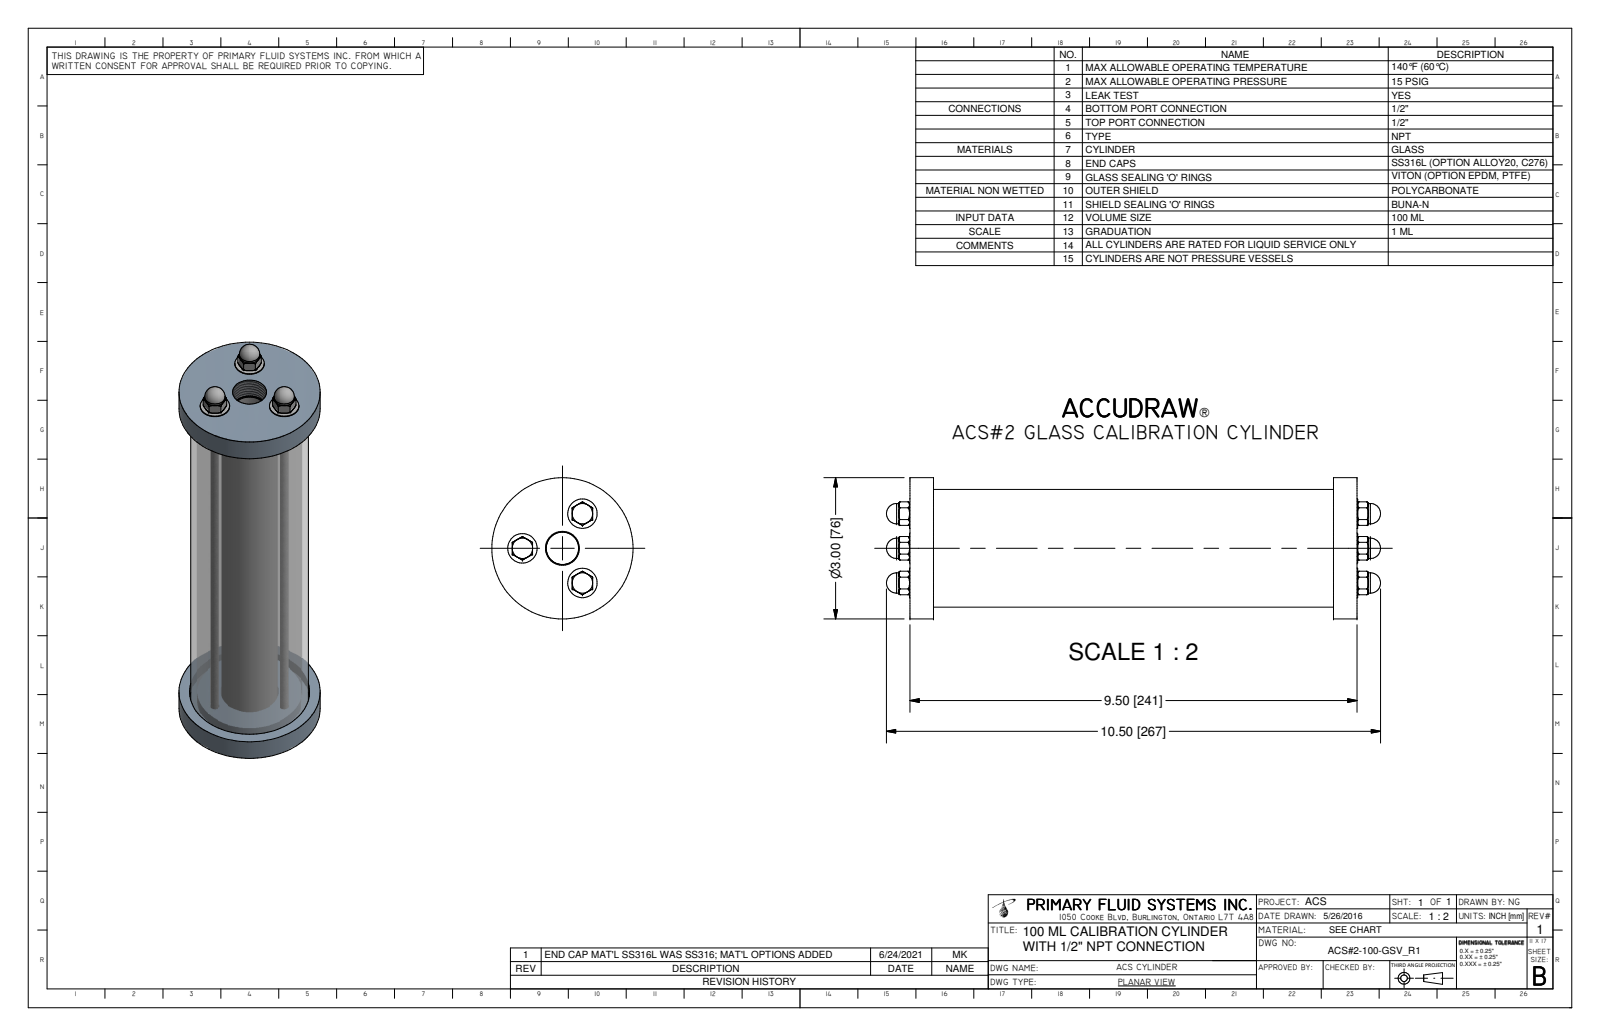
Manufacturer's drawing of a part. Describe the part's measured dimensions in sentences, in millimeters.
The part is named "ACS#2-100-GSV_R0; ACS-3-100-METAL_R3; ACS-2-100-PC_R6; ACS-1-100-A_R0 (+3 more)". Its 3-D file was written by "Autodesk Inventor 2009 (AUTOMOTIVE_DESIGN)". It is 19 solids with 429 faces: 38 planar, 41 cylindrical and 350 other. Overall it measures 266.7 by 76.2 by 76.2 millimeters. Its volume is 273 700 cubic millimeters and its surface area 180 600 square millimeters. Round holes: 3 of diameter 4.6, 3 of diameter 5.1, 3 of diameter 7.1, 1 of diameter 27.2, 1 of diameter 31, 1 of diameter 57.2, 1 of diameter 64.8. Round bosses or shafts: 3 of diameter 15.9, 3 of diameter 4.7, 1 of diameter 76.2, 1 of diameter 63.5, 1 of diameter 55.9, 1 of diameter 30, 1 of diameter 23.6. The main face-to-face distances are 12.7, 228.6, 241.3, 215.9, 5.7, 235.6, 7, 222.9, 6, 13. The hole center spacings are 21.6, 37.4, 37.4.
